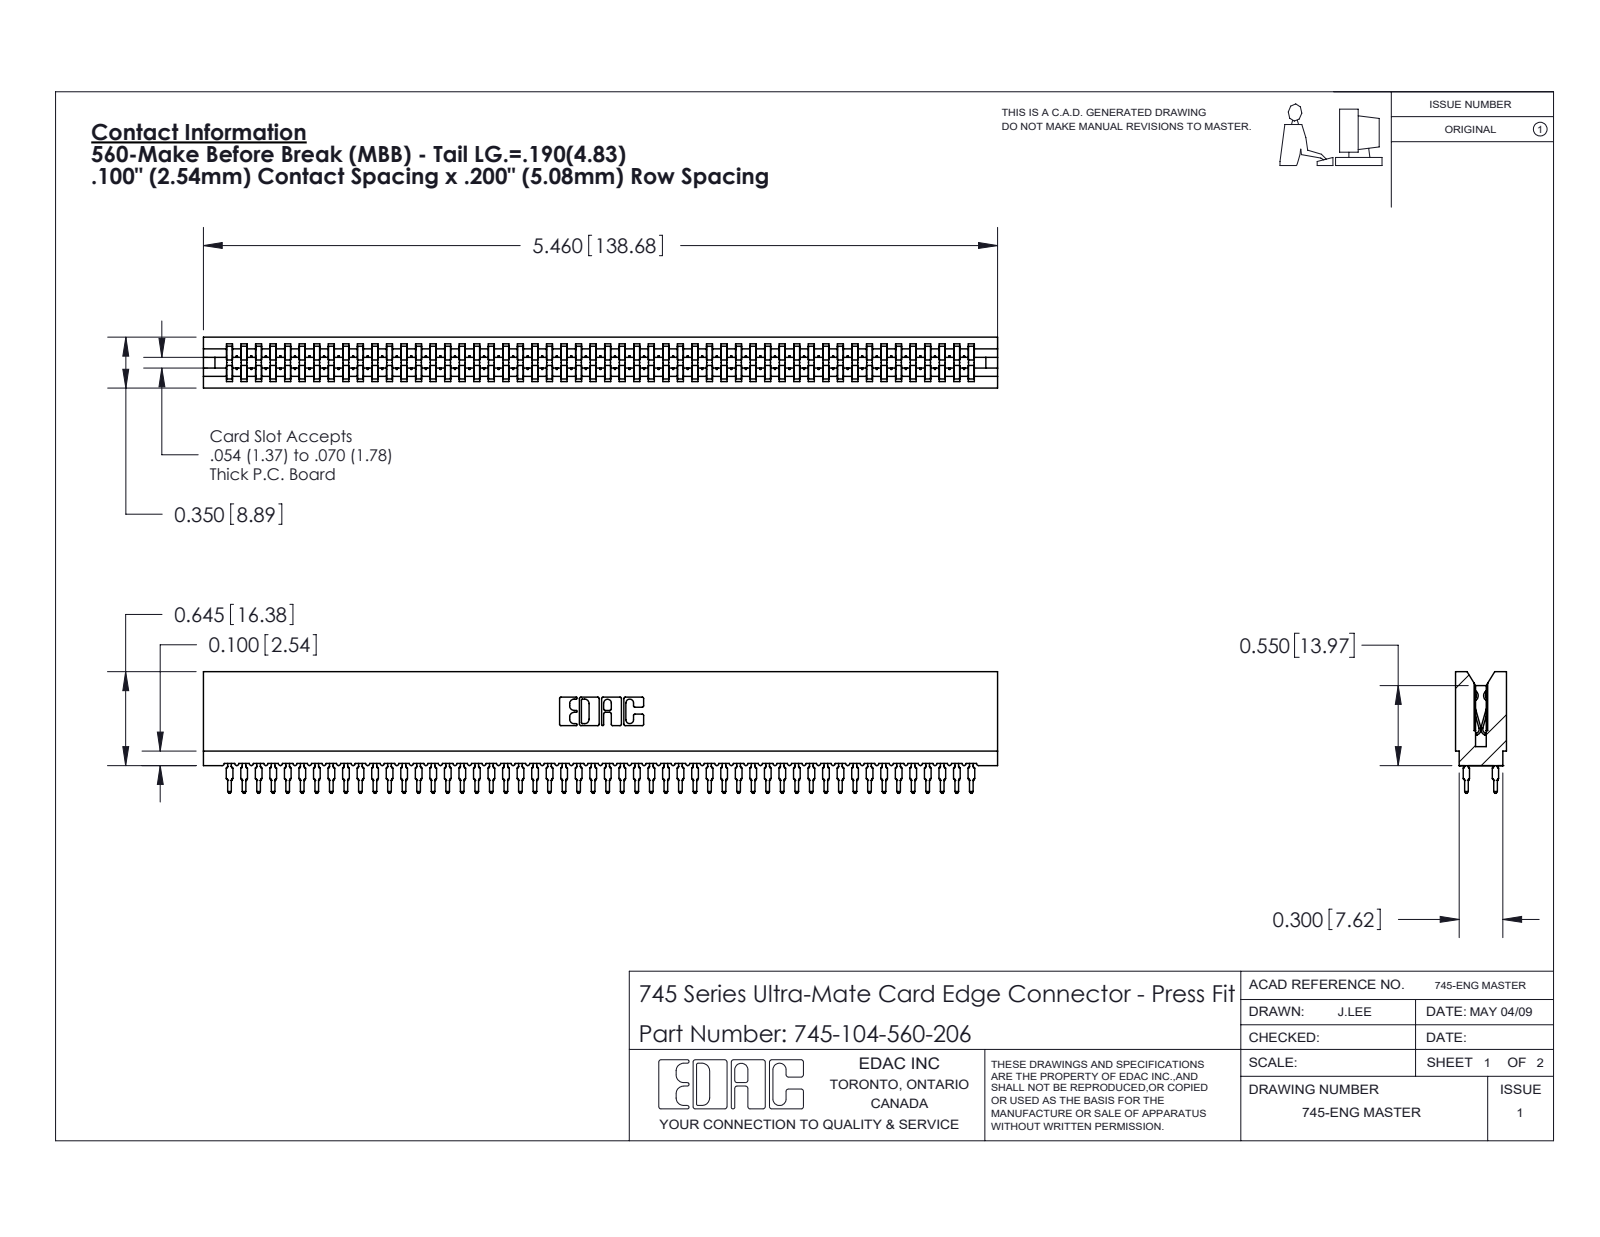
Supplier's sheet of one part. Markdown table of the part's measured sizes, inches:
| quantity | value |
| --- | --- |
| part name | 745-292-001_560; 745 Part_Insulator Option - 06; 745-104-560-206 |
| STEP written by | SolidWorks 2020 (CONFIG_CONTROL_DESIGN) |
| units | inches |
| bodies | 105 solids, 10340 faces (5360 planar, 2276 cylindrical, 2704 other) |
| overall size | 5.46 × 0.836 × 0.35 |
| volume | 0.781 in³ |
| surface area | 43.25 in² |
| partial cylindrical surfaces (radius × count) | 0.021 × 208, 0.015 × 104, 0.01 × 22, 0.005 × 8, 0.011 × 8, 0.007 × 6, 0.031 × 6, 0.026 × 3 |
| main face-to-face distances | 0.35, 0.063, 0.287, 0.2, 0.045, 0.305, 0.018, 0.243, 0.138, 0.212 |
